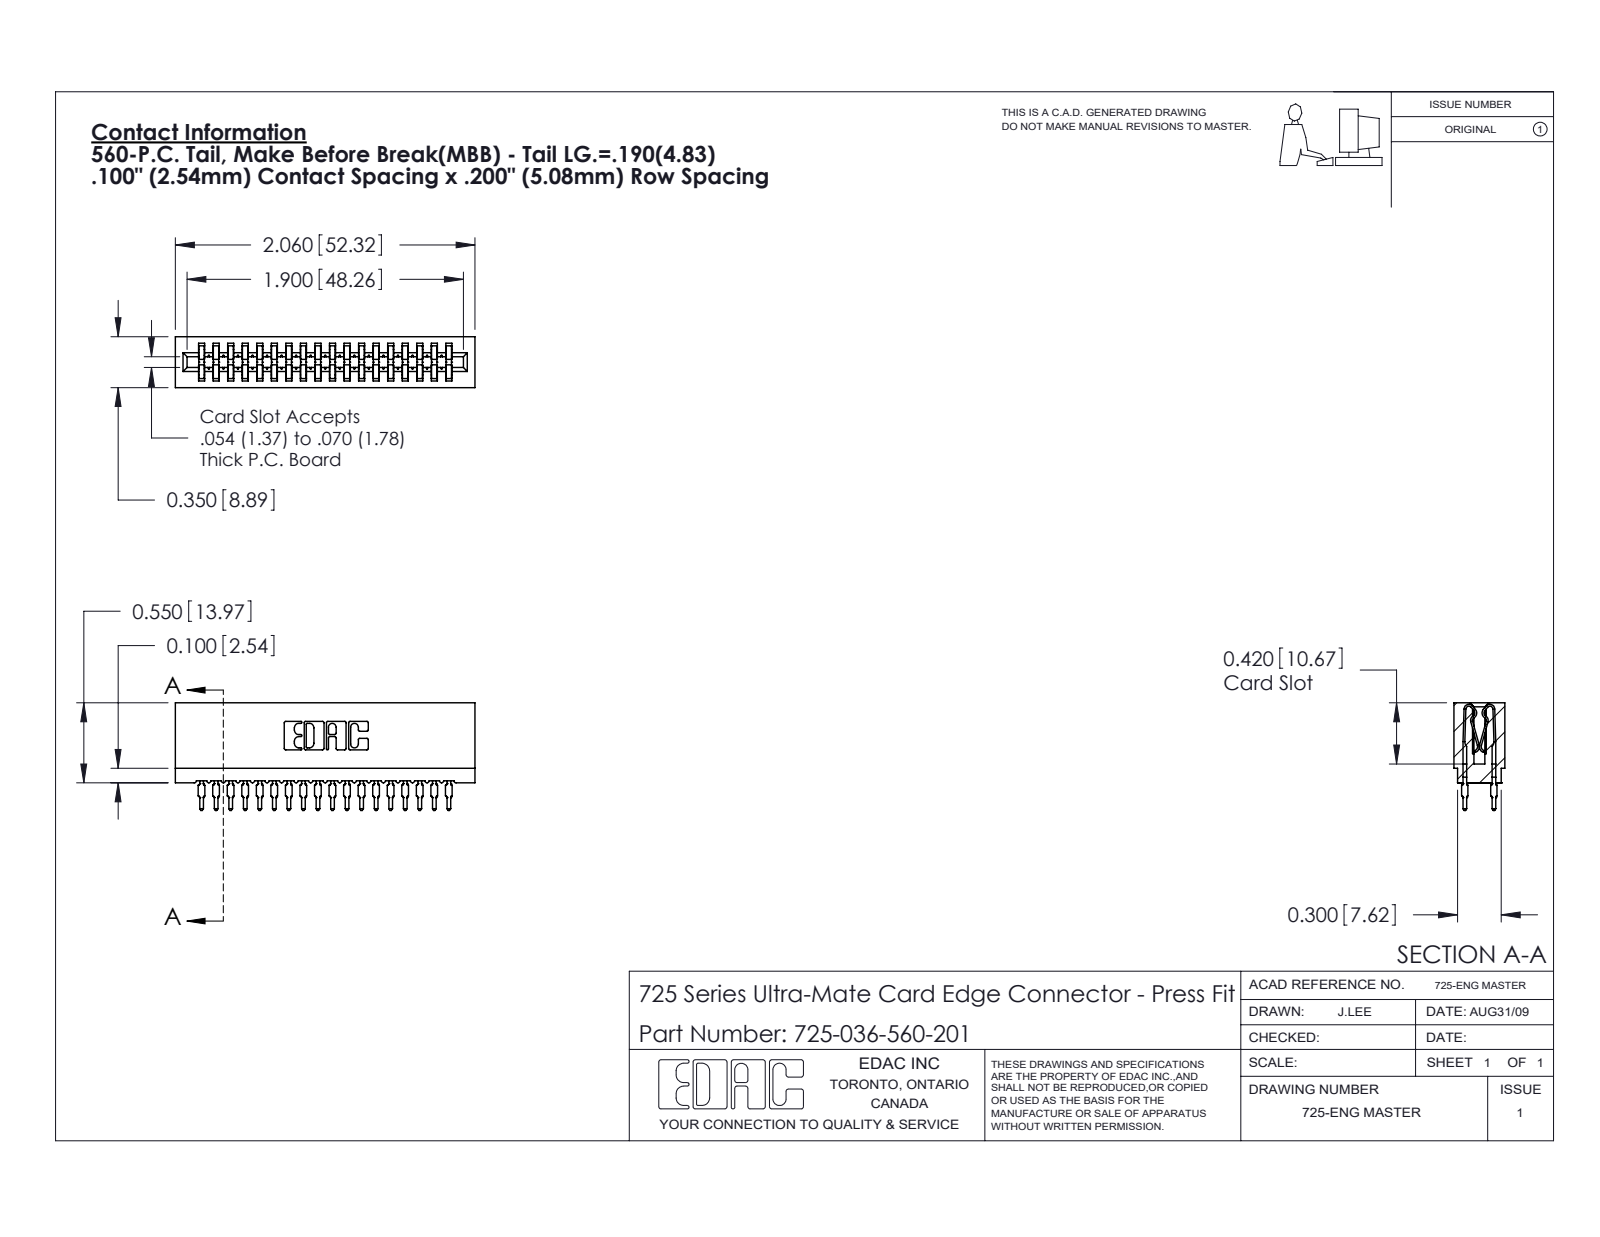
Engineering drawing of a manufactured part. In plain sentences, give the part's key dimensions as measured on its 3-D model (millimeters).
The part is named "725 Part_Insulator Option - 01; 745-292-001_560; 725-036-560-201". Its 3-D file was written by "SolidWorks 2020 (CONFIG_CONTROL_DESIGN)". It is 37 solids with 3641 faces: 1891 planar, 814 cylindrical and 936 other. Overall it measures 52.3 by 18.8 by 8.9 millimeters. Its volume is 4 410 cubic millimeters and its surface area 9 355 square millimeters. Partial cylindrical surfaces (rounded edges, fillets, slot ends): 72 of radius 0.5, 36 of radius 0.4, 22 of radius 0.3, 8 of radius 0.1, 8 of radius 0.3, 6 of radius 0.2, 6 of radius 0.8, 3 of radius 0.7. The main face-to-face distances are 5.1, 2.5, 7.6, 10.2, 12.7, 15.2, 17.8, 8.9, 1.6, 7.3.
